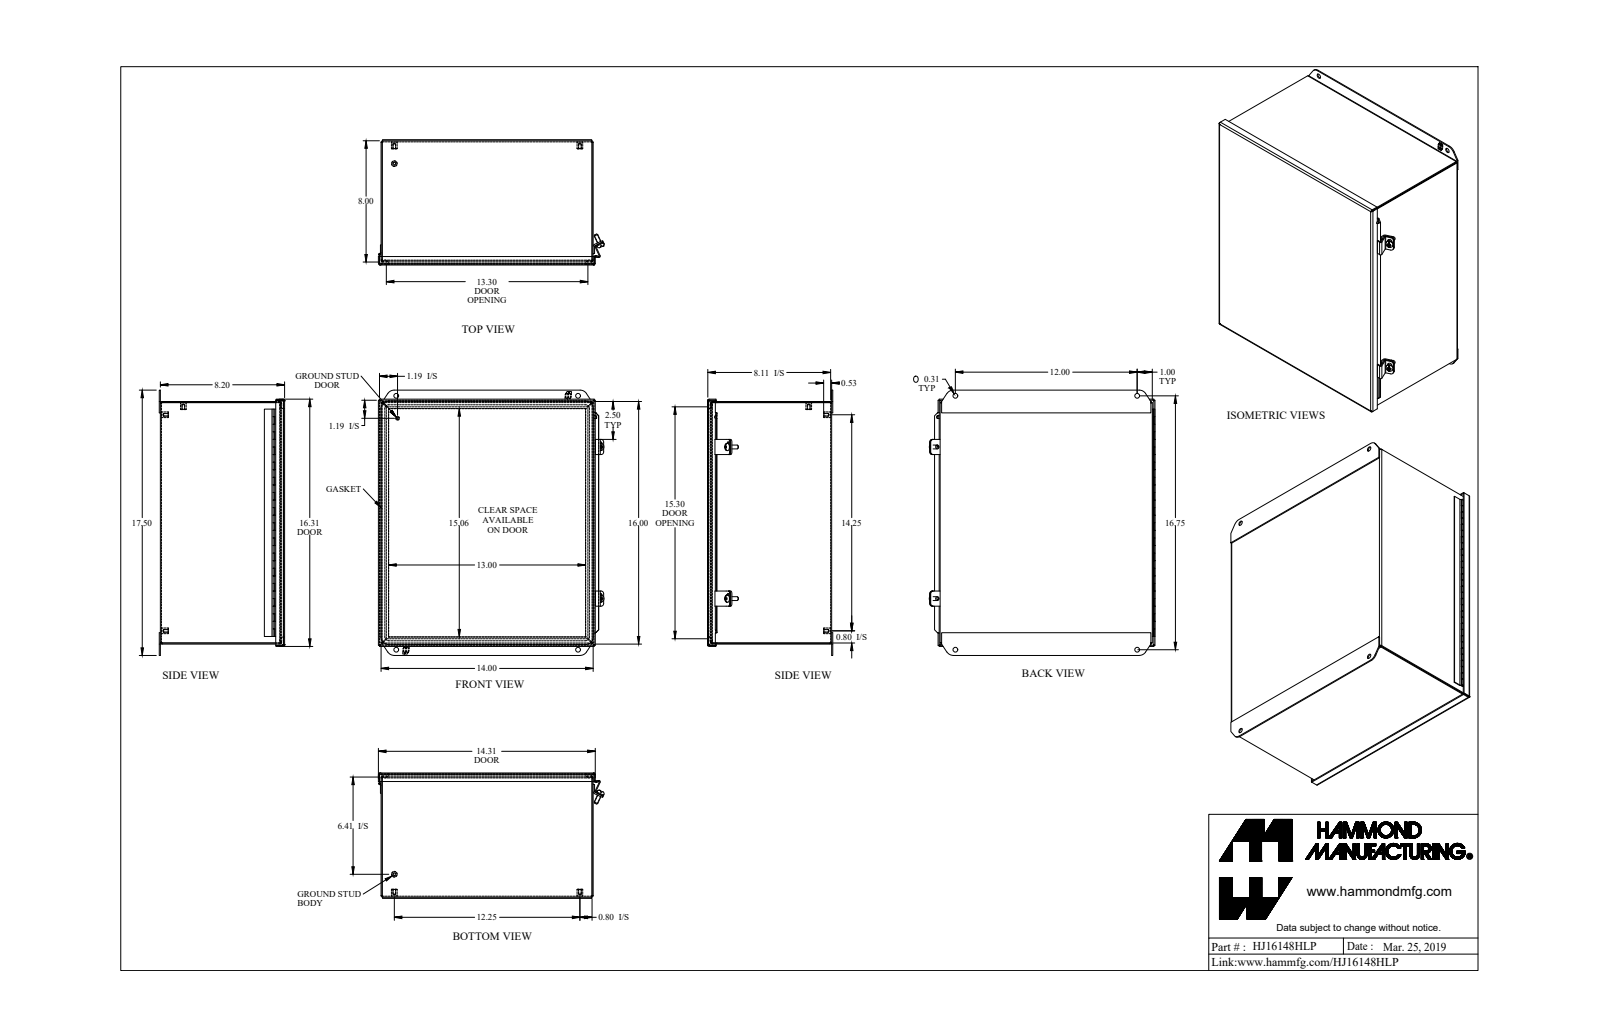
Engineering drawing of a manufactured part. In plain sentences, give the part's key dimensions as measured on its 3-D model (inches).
The part is named "HJ16148HLP". Its 3-D file was written by "SolidWorks 2018 (AUTOMOTIVE_DESIGN)". It is 20 solids with 841 faces: 446 planar, 267 cylindrical and 128 other. Overall it measures 17.5 by 14.896 by 8.269 inches. Its volume is 80.05 cubic inches and its surface area 2 243 square inches. Round holes: 5 of diameter 0.156, 4 of diameter 0.313, 2 of diameter 0.213, 1 of diameter 0.05. Round bosses or shafts: 5 of diameter 0.375, 3 of diameter 0.25, 2 of diameter 0.48, 1 of diameter 0.188, 1 of diameter 0.1, 1 of diameter 0.045. Partial cylindrical surfaces (rounded edges, fillets, slot ends): 16 of radius 0.25, 13 of radius 0.036, 13 of radius 0.108, 4 of radius 0.01, 4 of radius 0.141, 4 of radius 0.188, 4 of radius 0.499, 4 of radius 0.5. The main face-to-face distances are 0.072, 8.125, 8.197, 13.928, 8.053, 15.928, 13.856, 14, 16, 15.856. The hole center spacings are 1.256, 12.189, 15.5, 19.679, 12, 12.25, 14.25, 16.75.
